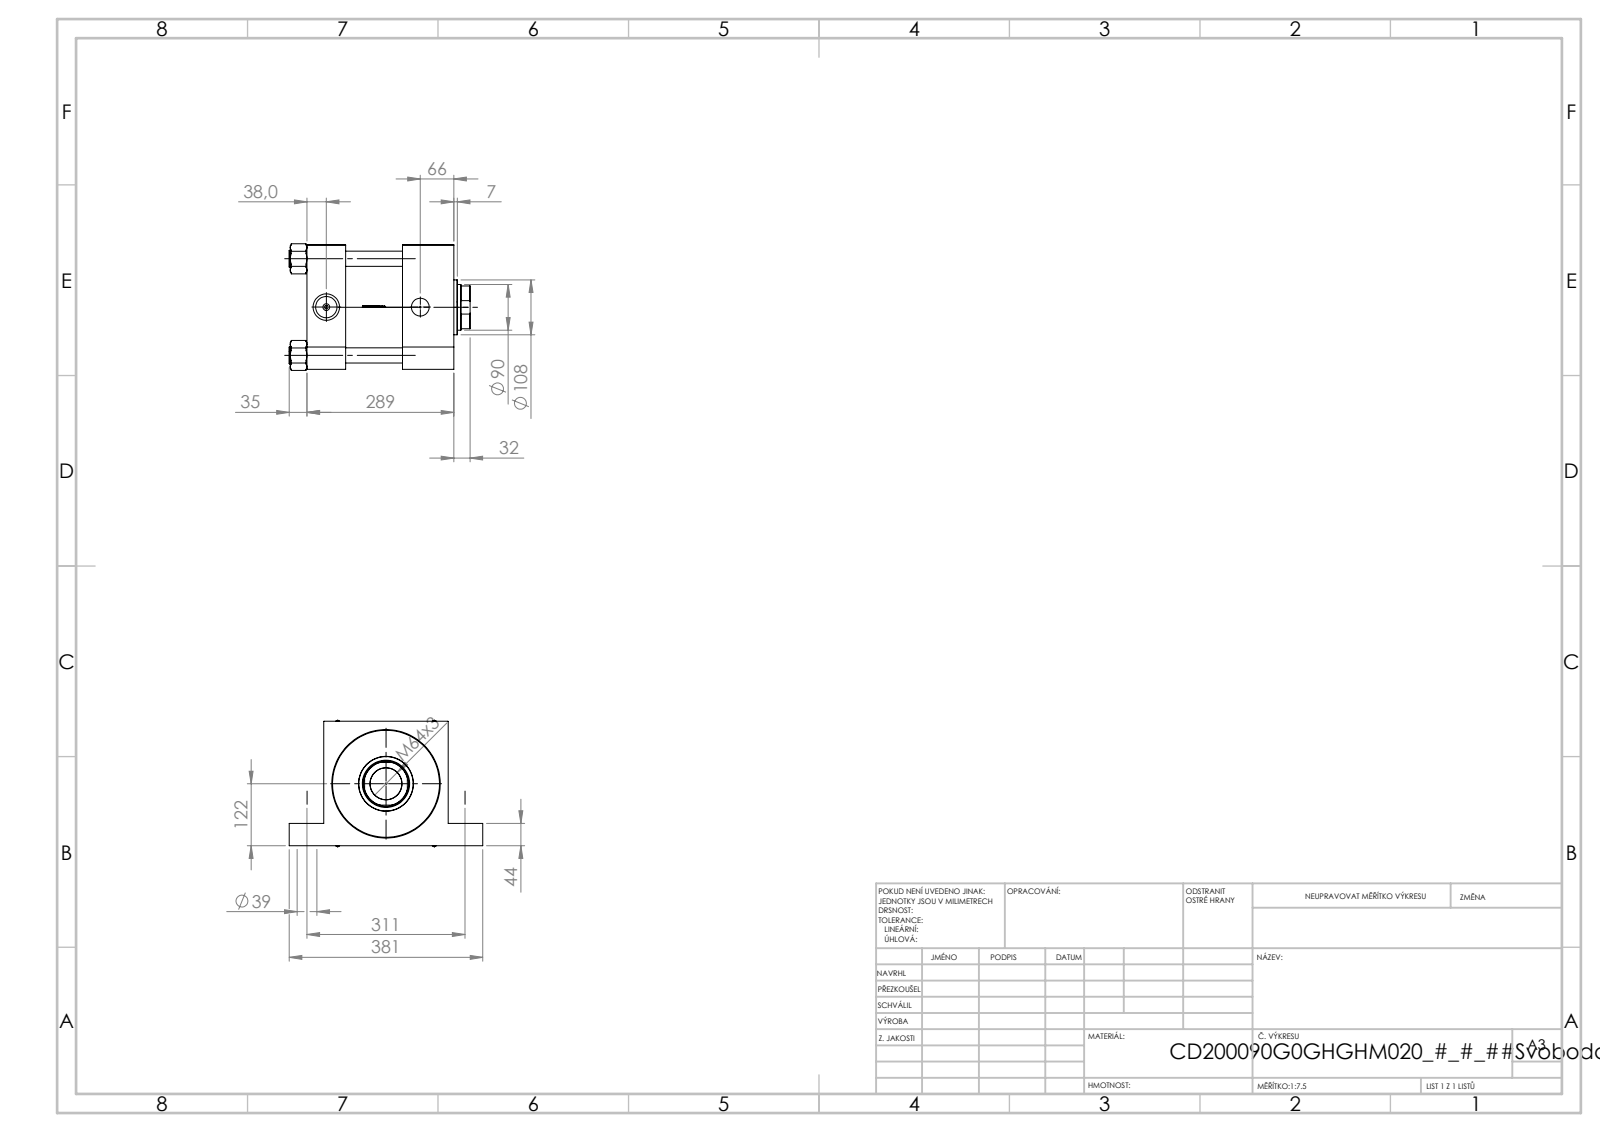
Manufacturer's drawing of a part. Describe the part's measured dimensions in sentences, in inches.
The part is named "V215CD_G_TYCINKA; V215CD_VC_G; V215CD_G_Body; V215CD_VCP_G (+1 more)". Its 3-D file was written by "SolidWorks 2019 (CONFIG_CONTROL_DESIGN)". It is 11 solids with 1135 faces: 479 planar, 124 cylindrical and 532 other. Overall it measures 15 by 14.016 by 9.82 inches. Its volume is 878.7 cubic inches and its surface area 1 719 square inches. Round holes: 4 of diameter 1.181, 4 of diameter 1.535, 2 of diameter 0.276, 2 of diameter 1.65, 1 of diameter 1.378, 1 of diameter 2.047, 1 of diameter 2.461, 1 of diameter 3.543, 1 of diameter 3.661, 1 of diameter 5.748, 1 of diameter 7.874, 1 of diameter 8.287. Round bosses or shafts: 4 of diameter 1.299, 1 of diameter 8.11, 1 of diameter 4.252. Partial cylindrical surfaces (rounded edges, fillets, slot ends): 1 of radius 1.732. The main face-to-face distances are 9.646, 2.992, 11.378, 8.386, 10.248, 7.256, 1.13, 3.976, 7.402, 4.409. The hole center spacings are 7.488, 5.281, 5.309, 7.559, 10.59, 12.244, 14.389, 7.283.
